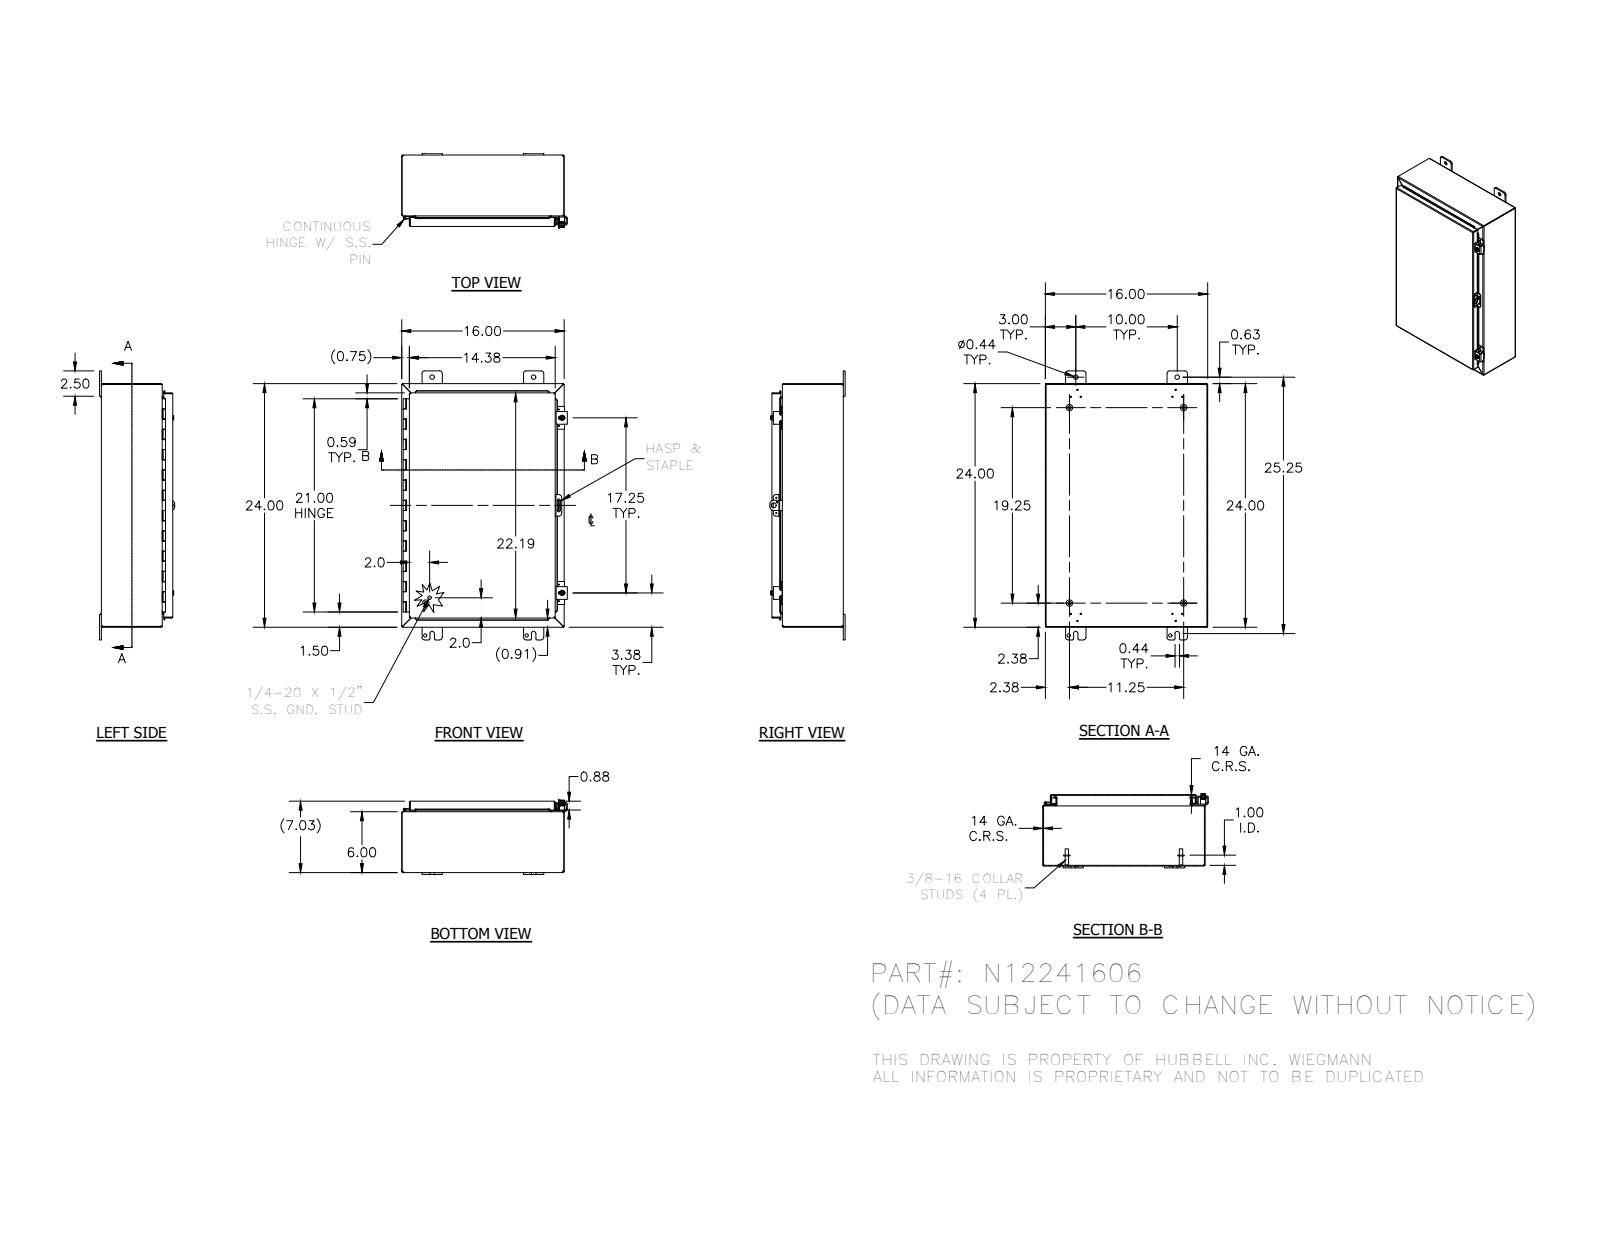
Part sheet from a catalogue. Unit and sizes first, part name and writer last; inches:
Units: inches
Overall size (bounding box): 26.5 × 16.311 × 7.41
Round holes (diameter × count): ⌀0.12 ×12, ⌀0.11 ×7, ⌀0.313 ×4, ⌀0.438 ×4, ⌀0.211 ×2, ⌀0.281 ×2, ⌀0.3 ×2, ⌀0.125 ×1, ⌀0.156 ×1, ⌀0.5 ×1
Round bosses / shafts (diameter × count): ⌀0.625 ×4, ⌀0.33 ×4, ⌀0.25 ×4, ⌀0.52 ×2, ⌀0.5 ×2, ⌀0.35 ×2, ⌀0.115 ×2, ⌀0.337 ×1
Partial cylindrical surfaces — rounded edges, fillets, slot ends (radius × count): R0.03 ×27, R0.063 ×25, R0.125 ×25, R0.25 ×25, R0.031 ×23, R0.105 ×23, R0.07 ×8, R0.1 ×4
Main face-to-face distances: 0.074, 6.959, 6.885, 7.033, 15.926, 5.926, 1.033, 23.926, 15.852, 16
Hole centre spacings: 10, 0.759, 0.839, 0.94, 0.969, 9.382, 10.348, 21.38
Volume: 119.5 in³ · Surface area: 3 098 in²
Bodies: 27 solids, 982 faces (533 planar, 332 cylindrical, 117 other)
Part name (STEP PRODUCT): N12241606; 34840; 38420; N12241606BKP (+8 more)
STEP written by: Autodesk Inventor 2012 (AUTOMOTIVE_DESIGN)
